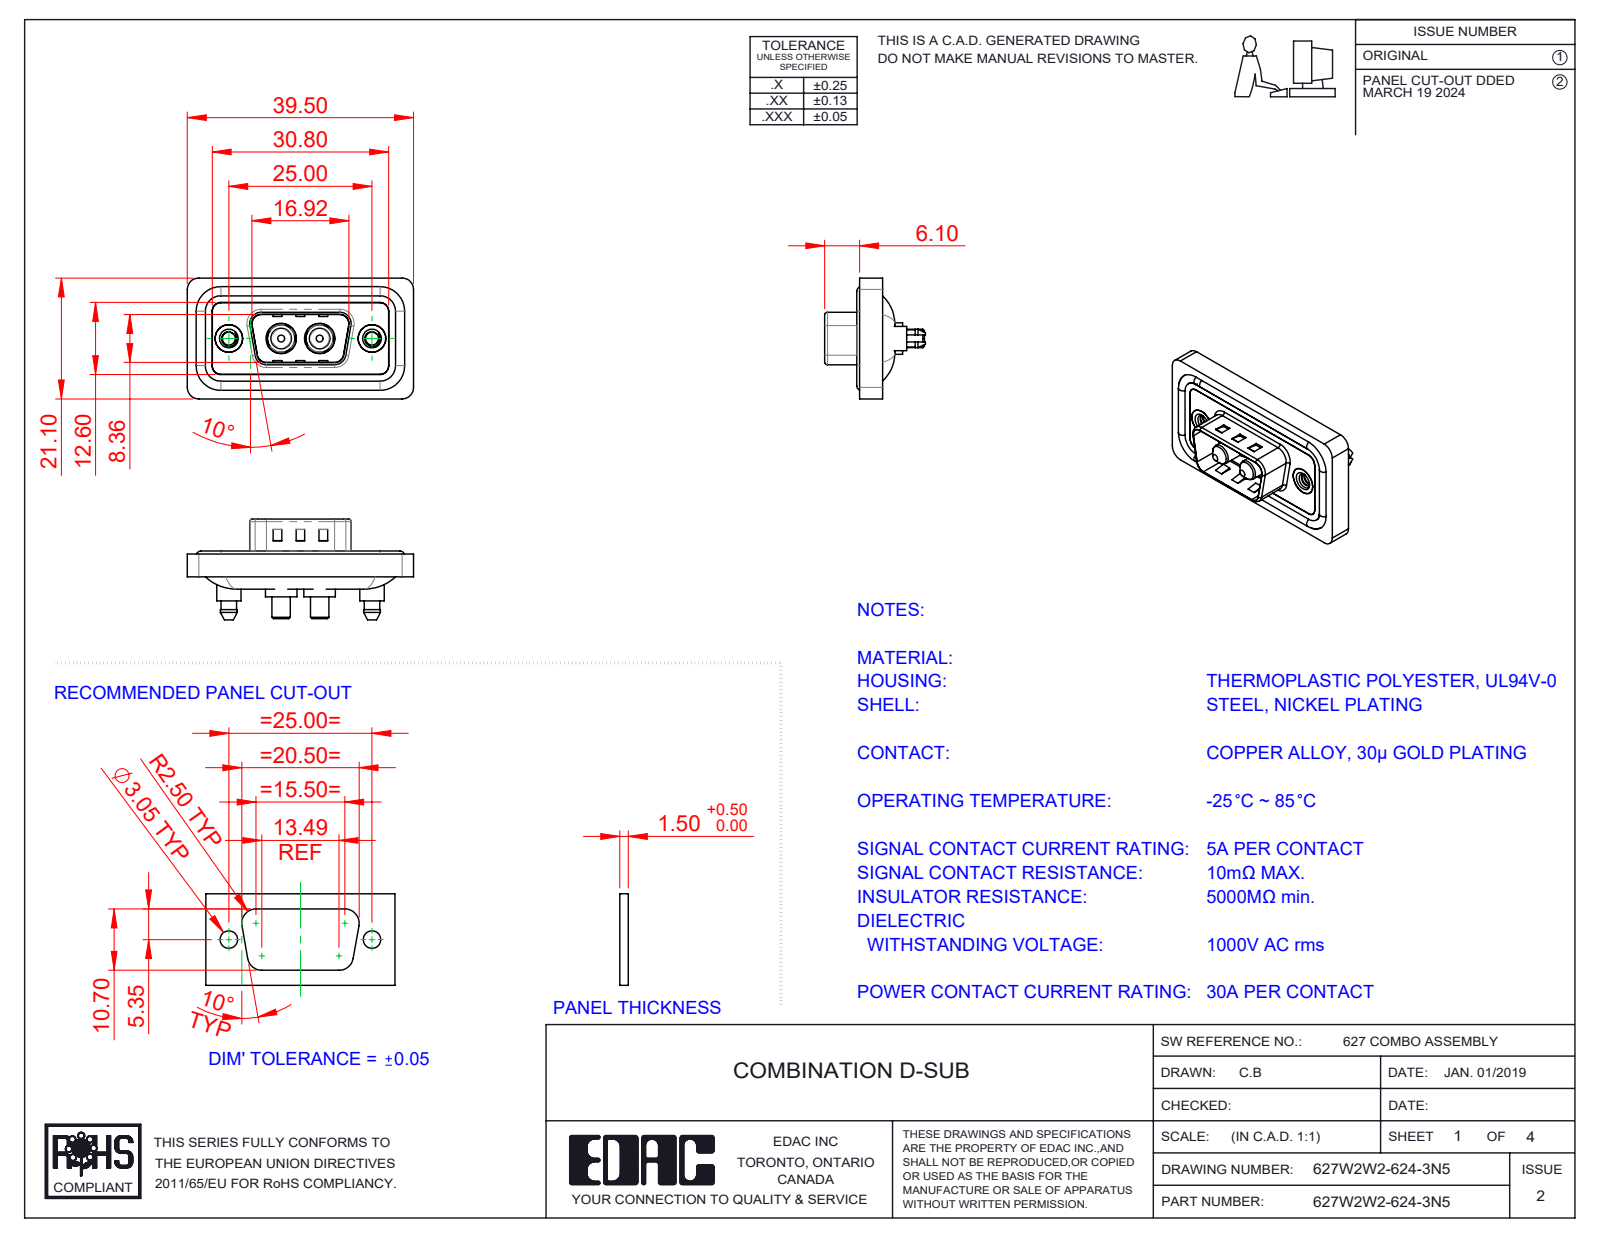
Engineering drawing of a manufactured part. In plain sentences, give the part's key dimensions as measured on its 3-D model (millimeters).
The part is named "Power Pin_30A S; 627W2W2-624-3N5; 627Combo Housing_2W2; 627Combo Shell Front_09 Contacts (+3 more)". Its 3-D file was written by "SolidWorks 2023 (CONFIG_CONTROL_DESIGN)". It is 11 solids with 539 faces: 181 planar, 250 cylindrical and 108 other. Overall it measures 39.5 by 21.1 by 17.6 millimeters. Its volume is 4 608 cubic millimeters and its surface area 7 326 square millimeters. Round holes: 2 of diameter 2.26, 2 of diameter 4, 2 of diameter 4.8, 2 of diameter 4.85, 2 of diameter 5, 2 of diameter 5.3. Round bosses or shafts: 4 of diameter 1.6, 2 of diameter 5.5, 2 of diameter 5.4, 2 of diameter 5.2, 2 of diameter 4.9, 2 of diameter 4.75, 2 of diameter 4.25, 2 of diameter 3.75. Partial cylindrical surfaces (rounded edges, fillets, slot ends): 24 of radius 1.5, 18 of radius 2, 10 of radius 1.6, 8 of radius 0.5, 4 of radius 0.25, 4 of radius 0.6, 4 of radius 0.65, 4 of radius 0.9. The main face-to-face distances are 0.4, 1.1, 2.9, 3.1, 0.5, 1.6, 1.5, 4, 0.7, 2.5. The hole center spacings are 9.14, 15.86, 6.72, 25.
